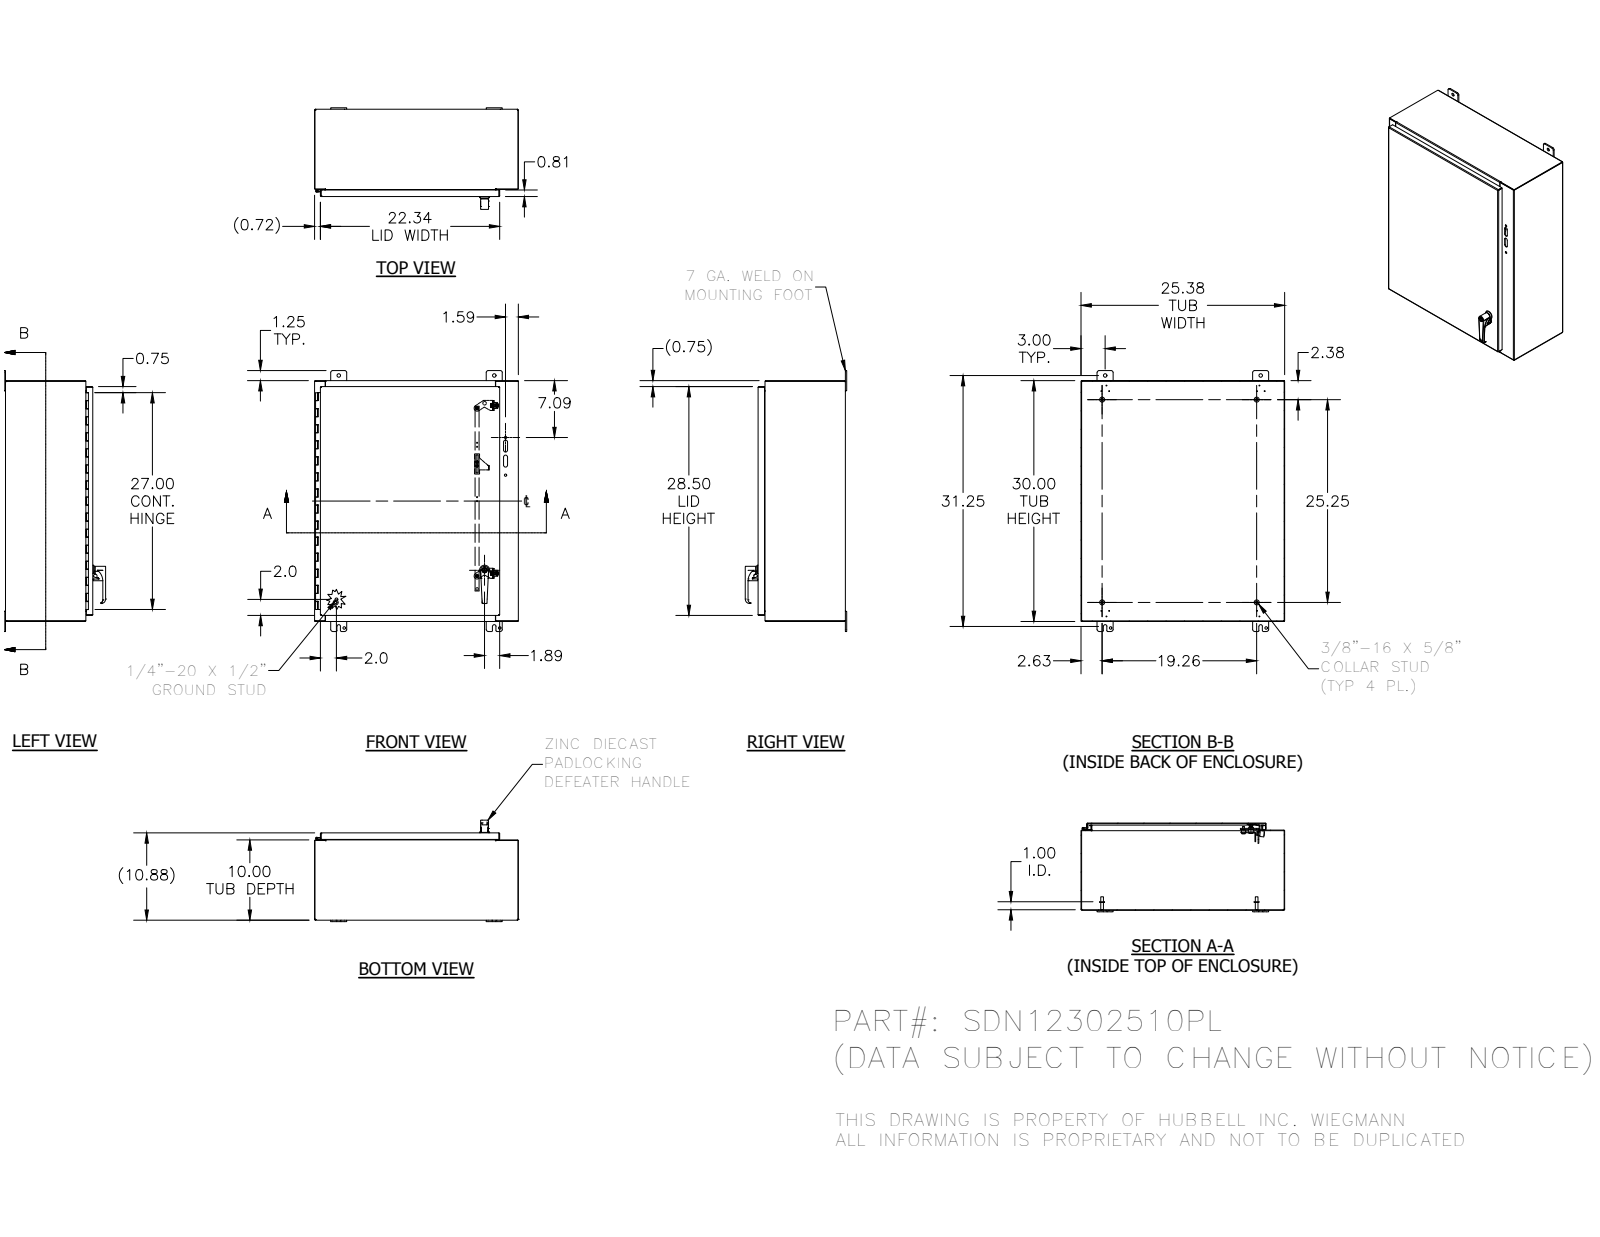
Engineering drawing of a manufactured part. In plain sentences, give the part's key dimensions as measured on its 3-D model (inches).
The part is named "SDN12302510PL; SDN12302510PLBKP; 388116; 34840 (+8 more)". Its 3-D file was written by "Autodesk Inventor 2012 (AUTOMOTIVE_DESIGN)". It is 49 solids with 1618 faces: 836 planar, 557 cylindrical and 225 other. Overall it measures 32.5 by 25.38 by 12.649 inches. Its volume is 222.8 cubic inches and its surface area 5 949 square inches. Round holes: 12 of diameter 0.12, 6 of diameter 0.145, 4 of diameter 0.313, 4 of diameter 0.438, 3 of diameter 0.32, 2 of diameter 0.156, 2 of diameter 0.196, 2 of diameter 0.211, 2 of diameter 0.22, 2 of diameter 0.281, 2 of diameter 0.313, 2 of diameter 0.45. Round bosses or shafts: 5 of diameter 0.625, 5 of diameter 0.33, 4 of diameter 0.437, 4 of diameter 0.3, 4 of diameter 0.25, 4 of diameter 0.225, 4 of diameter 0.19, 2 of diameter 0.75. Partial cylindrical surfaces (rounded edges, fillets, slot ends): 38 of radius 0.02, 31 of radius 0.012, 22 of radius 0.25, 20 of radius 0.031, 20 of radius 0.105, 16 of radius 0.025, 15 of radius 0.125, 8 of radius 0.07. The main face-to-face distances are 0.074, 10.801, 10.727, 10.875, 25.306, 29.926, 9.926, 0.875, 25.232, 25.38. The hole center spacings are 0.759, 1.593, 18.749, 19.38, 20.9, 27.38, 28.068, 28.069.
